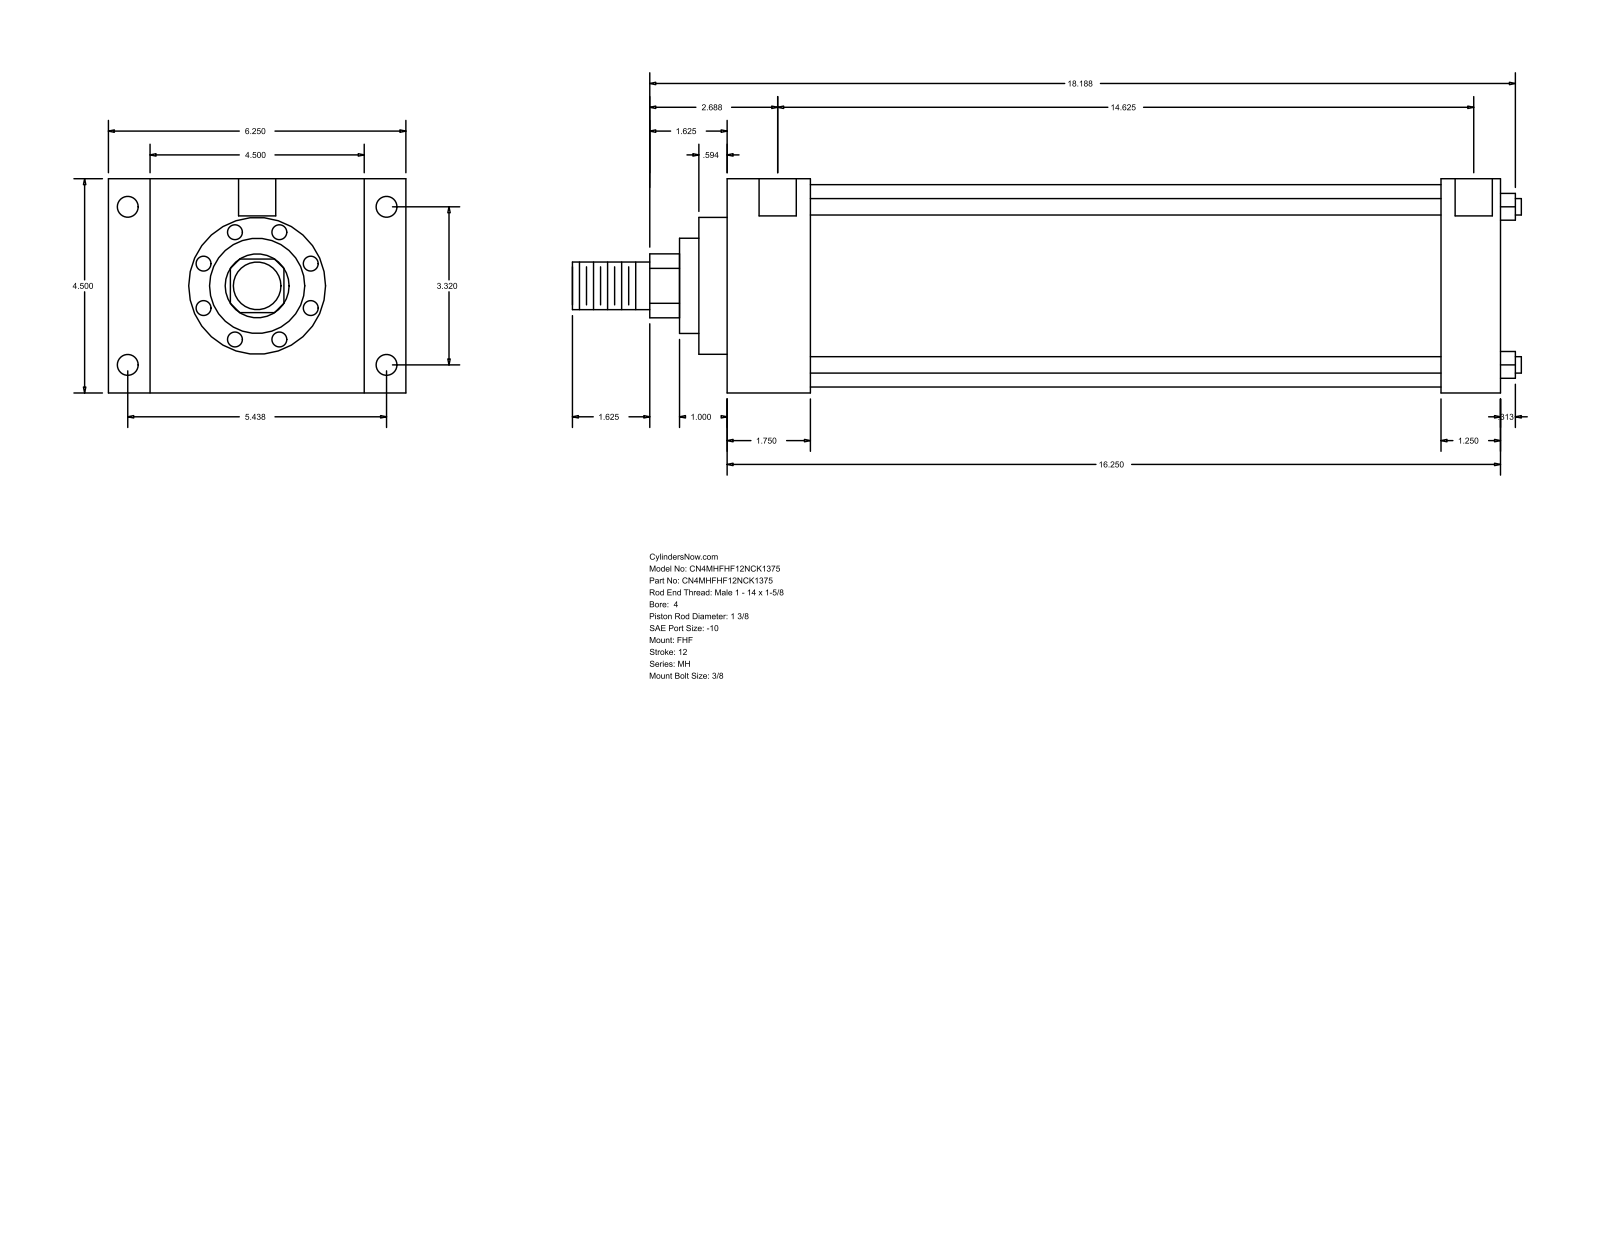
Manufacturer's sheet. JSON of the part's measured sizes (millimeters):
{"part_name": "MH_FHF__0400_1.375", "step_written_by": "GSSL Pune (CONFIG_CONTROL_DESIGN)", "units": "millimeters", "bodies": {"solids": 0, "faces": 90, "planar": 61, "cylindrical": 29, "other": 0}, "overall_size": [506.41, 158.75, 114.3], "round_holes": [[8.73, 4], [11.13, 4], [19.84, 2]], "round_bosses_or_shafts": [[8.76, 4], [107.95, 1], [73.03, 1], [50.8, 1], [34.92, 1], [25.4, 1]], "partial_cylinders_radius": [[17.06, 1]], "face_to_face_distances": [114.3, 412.75, 44.45, 368.3, 22.23, 136.53, 158.76, 381, 336.55, 31.75], "hole_center_spacings": [84.32, 138.12, 161.82, 374.65, 1.58, 1.59, 371.48, 373.06]}
